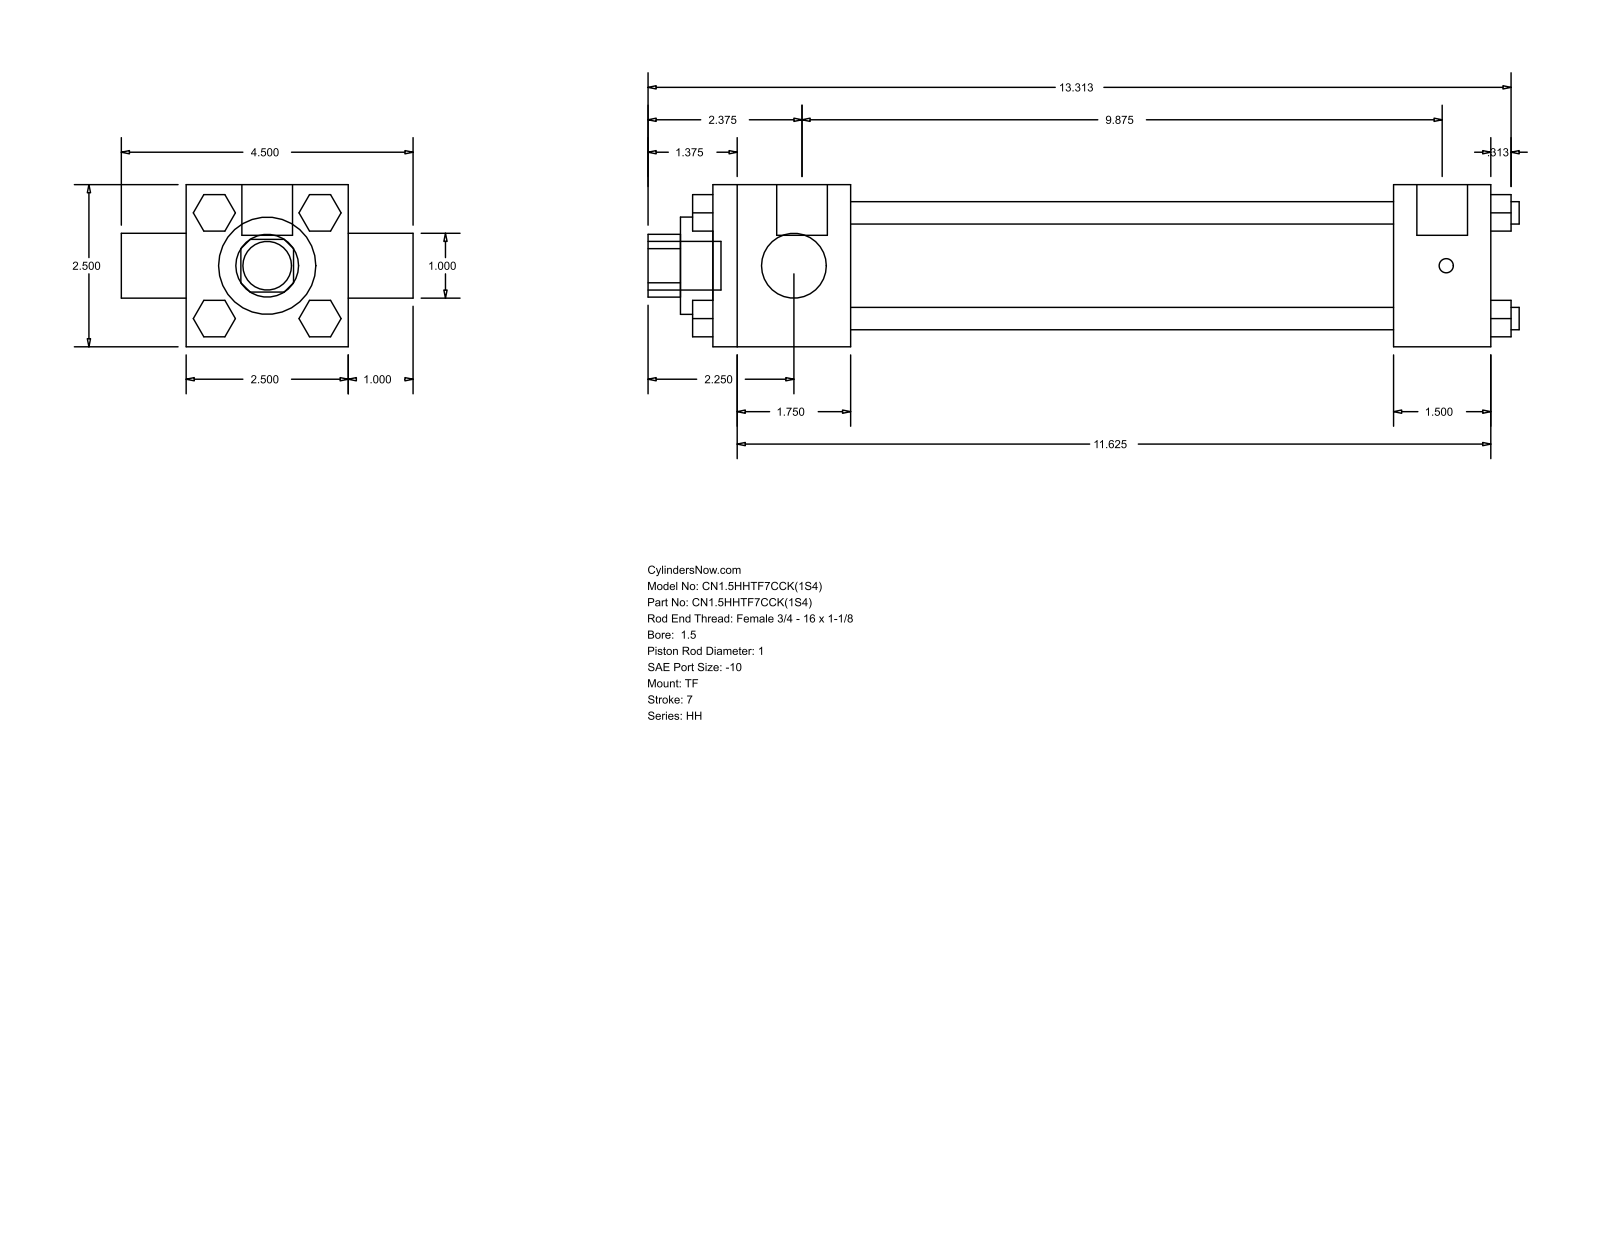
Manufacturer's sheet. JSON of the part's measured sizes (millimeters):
{"part_name": "HH_TF__0150_1", "step_written_by": "GSSL Pune (CONFIG_CONTROL_DESIGN)", "units": "millimeters", "bodies": {"solids": 0, "faces": 120, "planar": 92, "cylindrical": 28, "other": 0}, "overall_size": [341.31, 114.3, 63.5], "round_holes": [[25.4, 2], [38.1, 1], [44.45, 1]], "round_bosses_or_shafts": [[8.76, 4], [5.56, 3], [19.84, 2], [19.05, 1]], "partial_cylinders_radius": [[12.29, 1]], "face_to_face_distances": [63.5, 250.82, 212.72, 38.1, 53.98, 266.7, 304.8, 312.74, 25.4, 20.7]}
